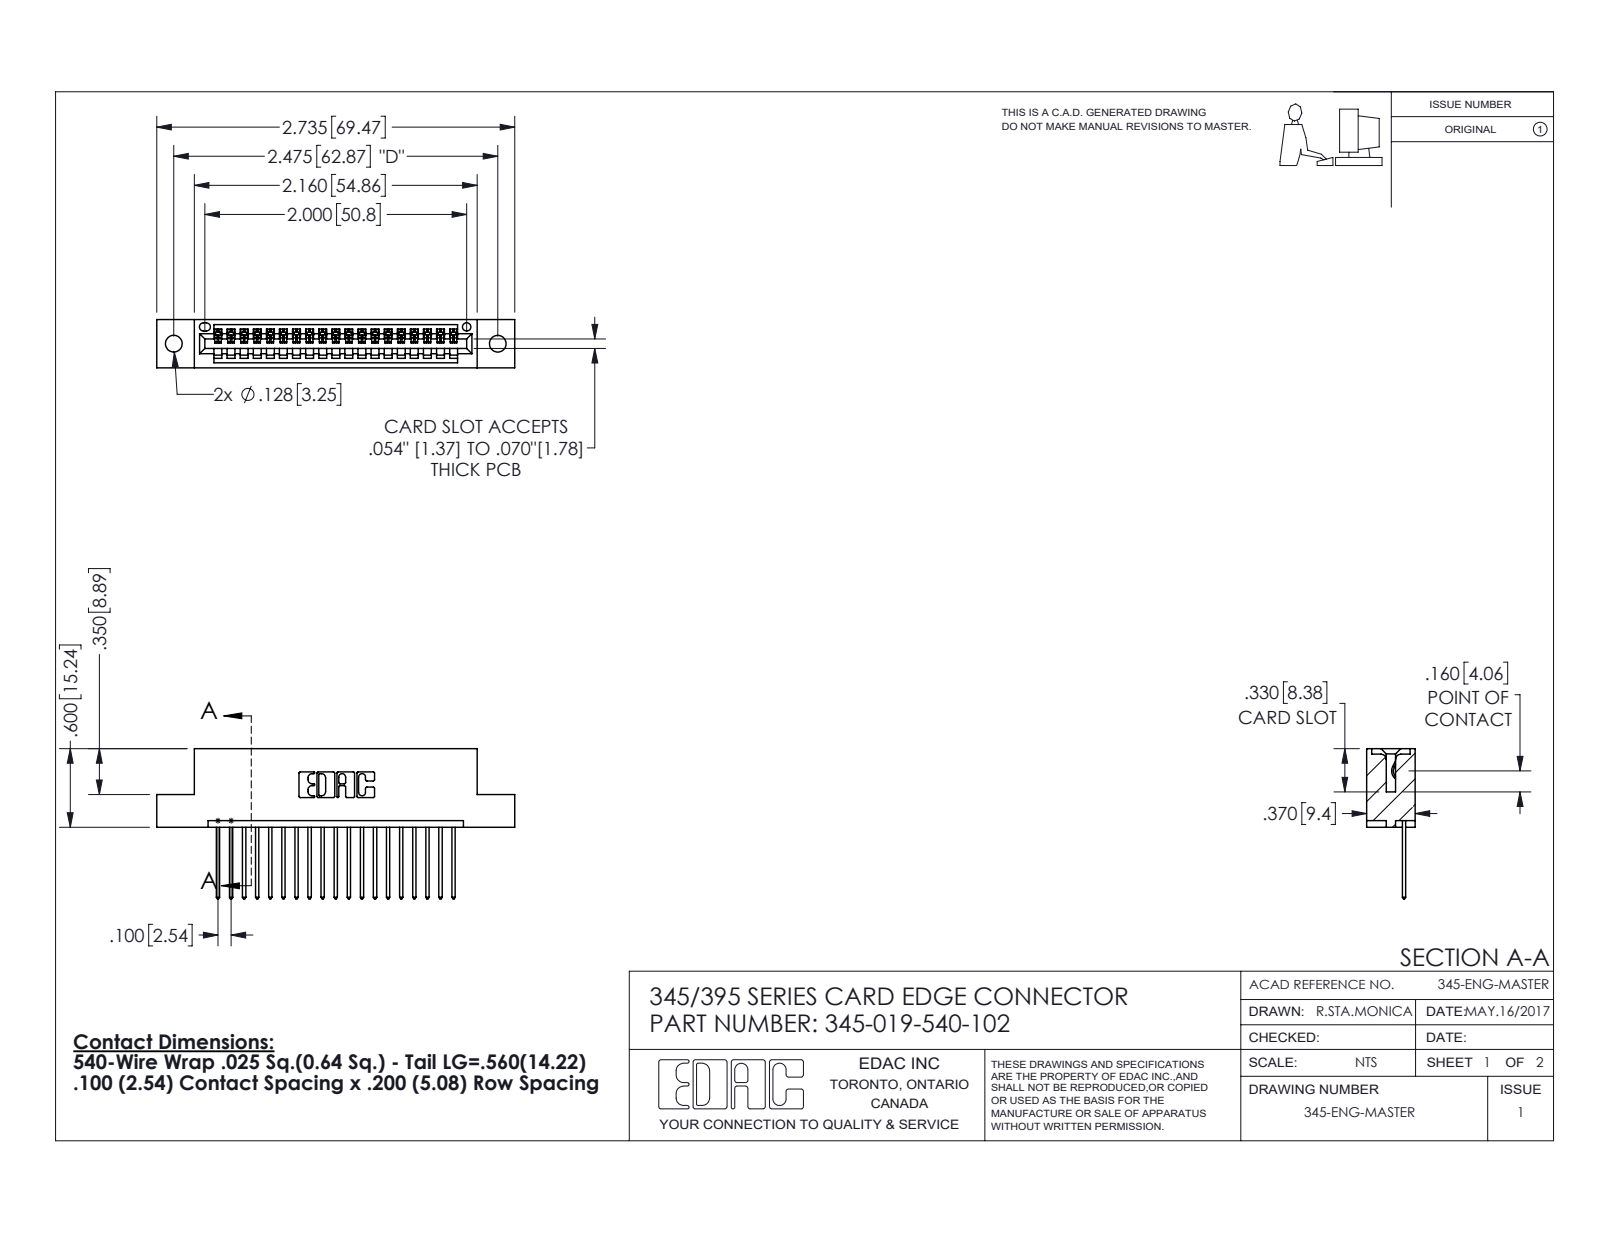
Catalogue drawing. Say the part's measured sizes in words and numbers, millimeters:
The part is named "345-292-001_345-293-140; 345 Part_Flush Mounting Lugs - 0.128 Dia; 345-019-540-102". Its 3-D file was written by "SolidWorks 2016 (CONFIG_CONTROL_DESIGN)". It is 20 solids with 1228 faces: 840 planar, 388 cylindrical and 0 other. Overall it measures 69.5 by 29.1 by 9.4 millimeters. Its volume is 6 390 cubic millimeters and its surface area 8 103 square millimeters. Round holes: 2 of diameter 3.3, 1 of diameter 1.6. Partial cylindrical surfaces (rounded edges, fillets, slot ends): 38 of radius 0.2, 38 of radius 0.3, 22 of radius 0.3, 6 of radius 0.2, 6 of radius 0.8, 3 of radius 0.7, 2 of radius 0.8, 2 of radius 1. The main face-to-face distances are 7.6, 1.8, 5.1, 9.4, 2.5, 6.9, 0.6, 5.7, 15.2, 3.8. The hole center spacings are 6.9, 56.9, 62.9.
